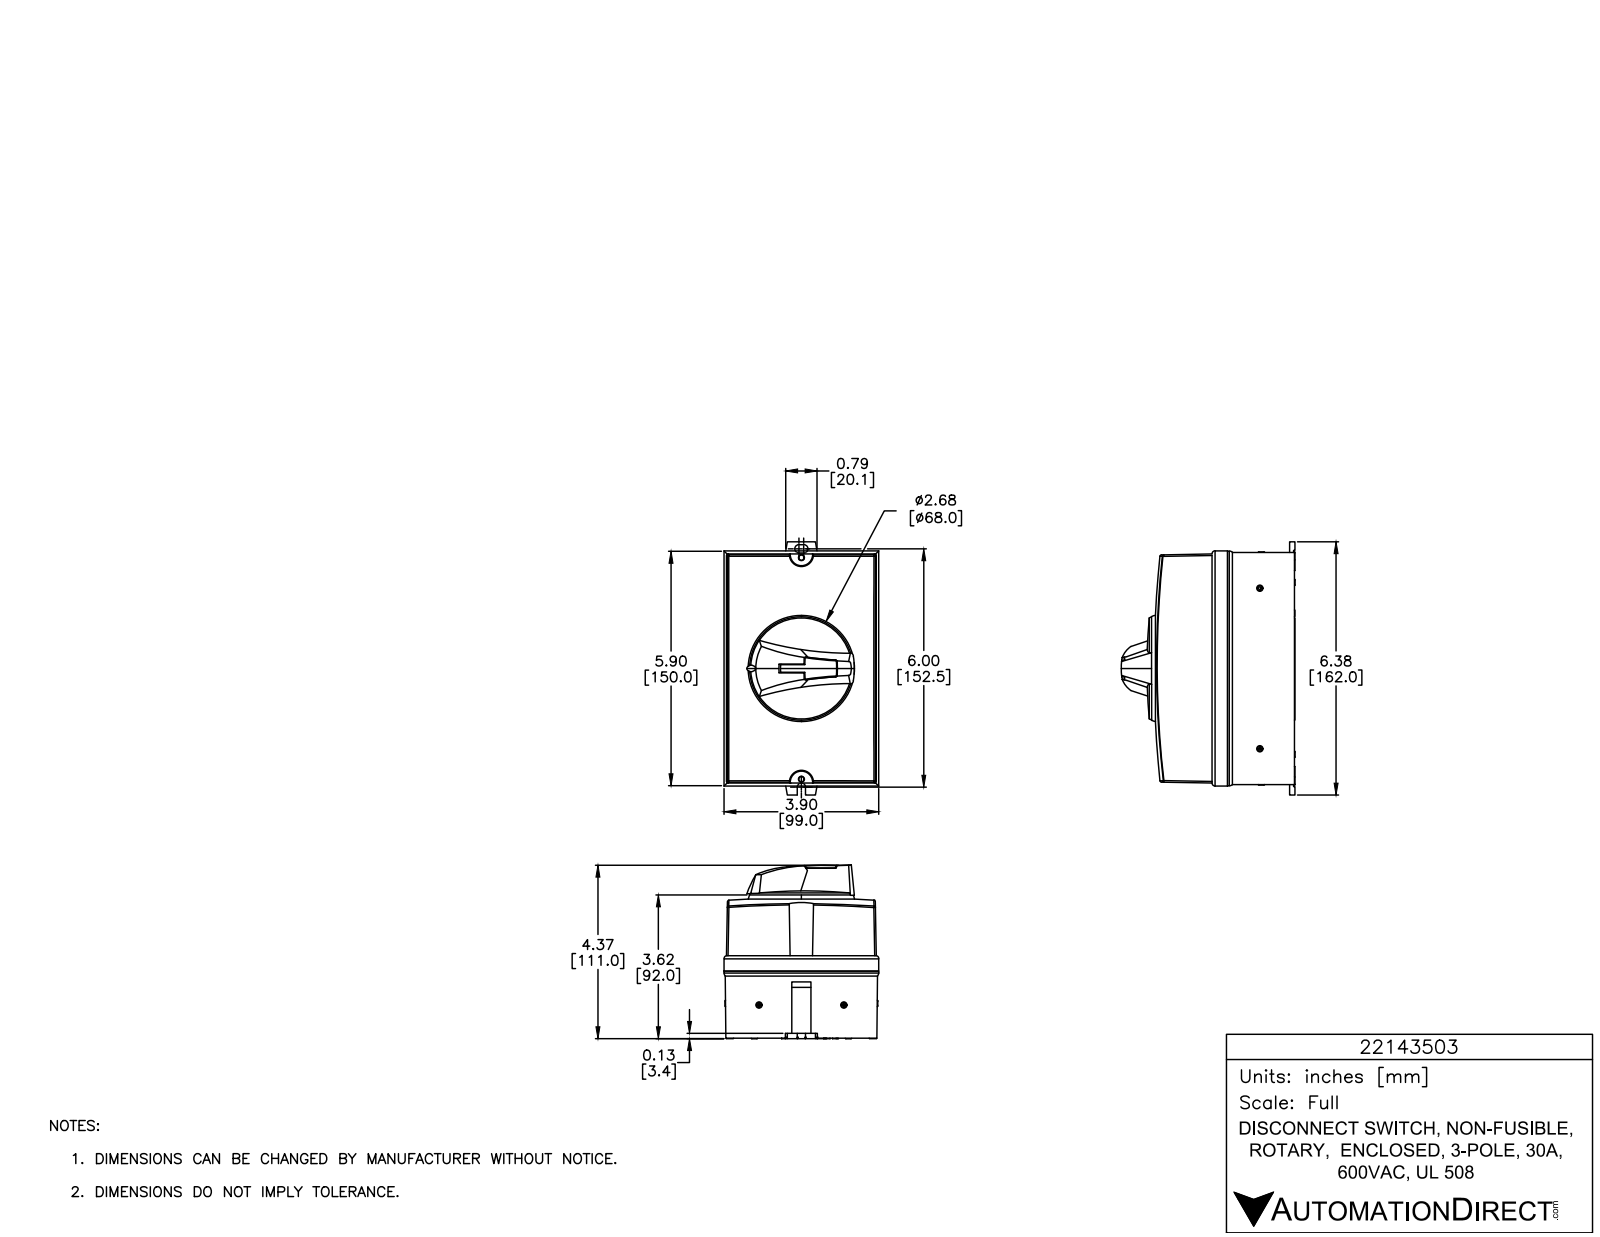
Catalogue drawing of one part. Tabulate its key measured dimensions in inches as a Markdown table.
| quantity | value |
| --- | --- |
| part name | 22143503 |
| STEP written by | SolidWorks 2015 (AUTOMOTIVE_DESIGN) |
| units | inches |
| bodies | 7 solids, 3173 faces (2559 planar, 285 cylindrical, 329 other) |
| overall size | 6.386 × 4.38 × 3.901 |
| volume | 27.12 in³ |
| surface area | 305.7 in² |
| round holes (diameter × count) | 0.26 × 6, 0.134 × 2, 0.15 × 2, 0.102 × 1, 0.339 × 1, 1.26 × 1, 2.535 × 1 |
| round bosses / shafts (diameter × count) | 0.197 × 8, 0.142 × 6, 0.315 × 2, 2.772 × 1, 1.244 × 1, 0.371 × 1, 0.189 × 1, 0.091 × 1 |
| partial cylindrical surfaces (radius × count) | 0.006 × 64, 0.008 × 8, 0.197 × 7, 0.209 × 6, 0.039 × 5, 0.079 × 5, 0.118 × 4, 0.02 × 3 |
| main face-to-face distances | 0.118, 0.119, 3.102, 1.689, 1.571, 2.984, 1.413, 5.846, 1.531, 1.584 |
| hole center spacings | 0.591, 1.219, 1.821, 2.214, 3.901, 2.134, 1.067, 1.181 |
